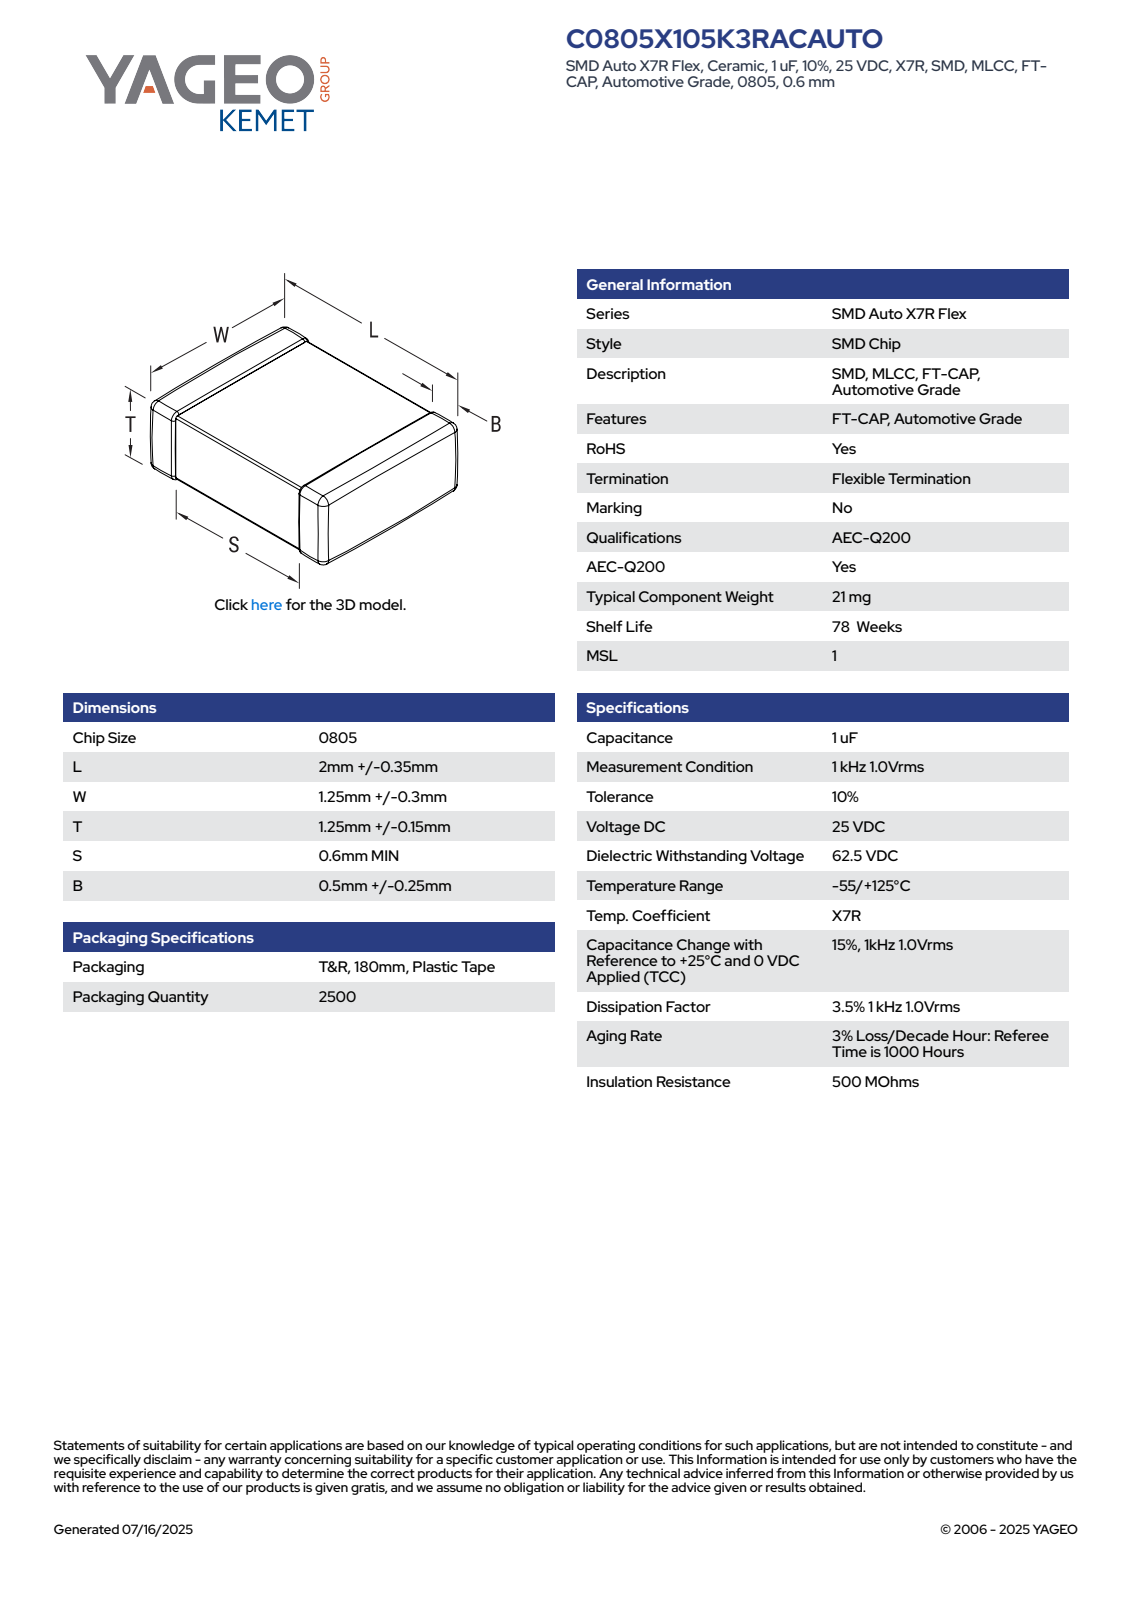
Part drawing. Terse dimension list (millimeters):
name: CCS_CCSTD_0805_L2.35W1.55T1.4B0.5
written by: SolidWorks 2014 (AUTOMOTIVE_DESIGN)
unit: mm
bodies: 4 solids, 125 faces (71 planar, 38 cylindrical, 16 other)
size: 2.35 × 1.55 × 1.4
volume: 5 mm³; area: 18 mm²
face distances: 1.37, 1.52, 2.35, 1.34, 1.49, 1.4, 1.55, 1.04, 1.31, 1.08
